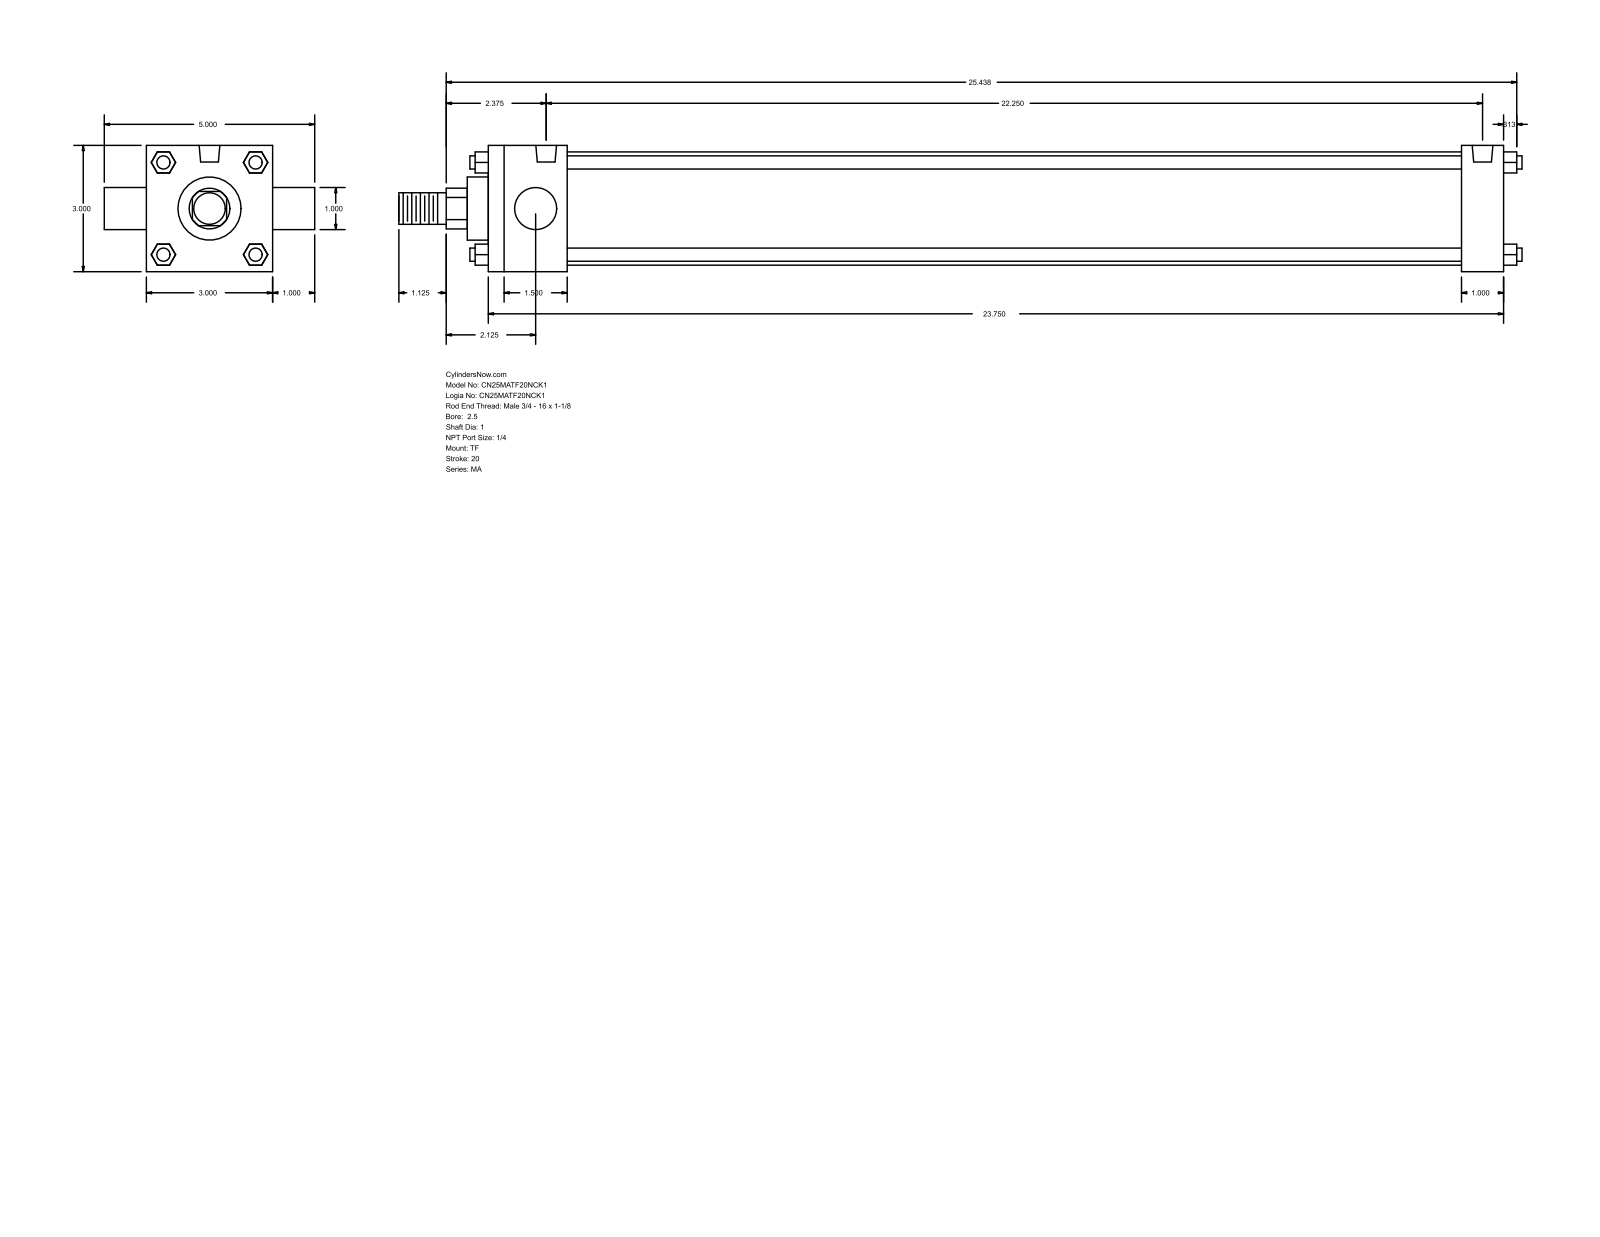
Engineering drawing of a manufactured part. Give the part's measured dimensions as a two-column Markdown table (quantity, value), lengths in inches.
| quantity | value |
| --- | --- |
| part name | MA_TF__0250_1 |
| STEP written by | GSSL Pune (CONFIG_CONTROL_DESIGN) |
| units | inches |
| bodies | 0 solids, 120 faces (92 planar, 28 cylindrical, 0 other) |
| overall size | 26.687 × 5 × 3 |
| round holes (diameter × count) | 0.313 × 3, 0.492 × 2 |
| round bosses / shafts (diameter × count) | 0.313 × 4, 1 × 2, 2.69 × 1, 1.5 × 1, 0.75 × 1 |
| partial cylindrical surfaces (radius × count) | 0.484 × 1 |
| main face-to-face distances | 3, 24.125, 1, 0.5, 1.875, 23.125, 21.25, 22.25, 4, 1.095 |
| hole center spacings | 22.25 |
